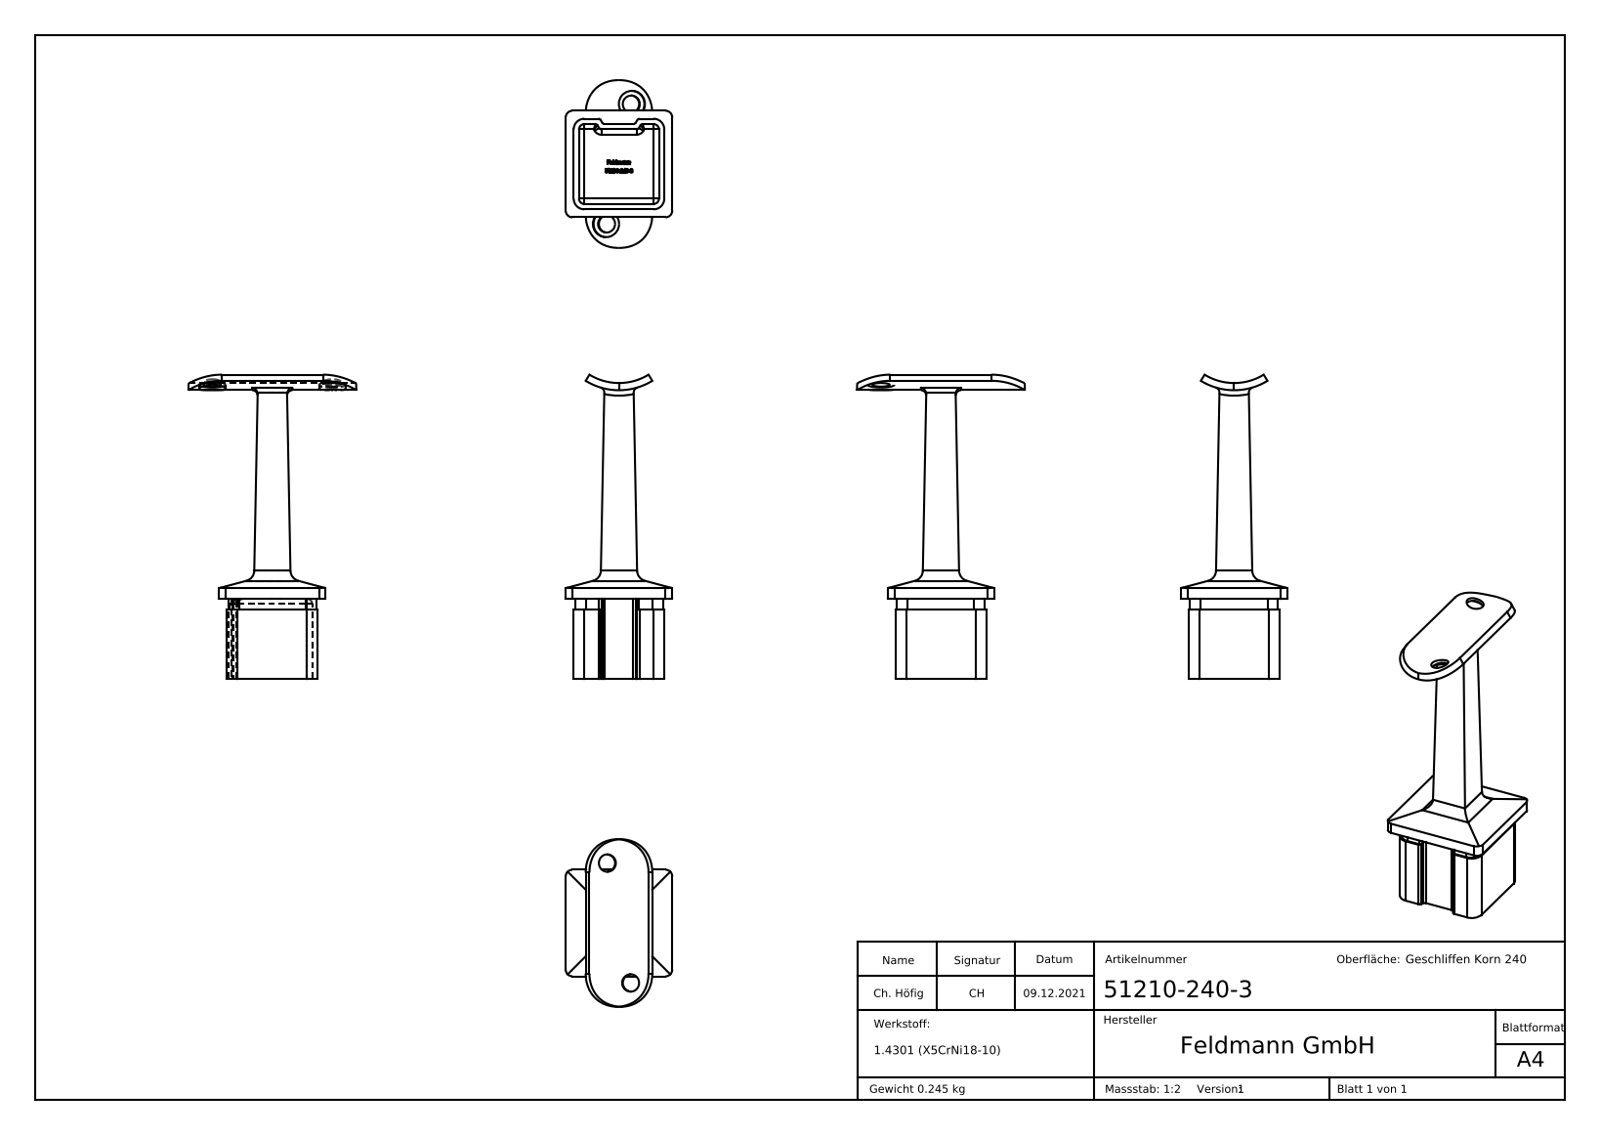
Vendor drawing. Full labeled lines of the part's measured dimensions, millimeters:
Part name (STEP PRODUCT): 51210-240-3
STEP written by: SolidWorks 2018 (CONFIG_CONTROL_DESIGN)
Units: millimetres
Bodies: 1 solid, 334 faces (174 planar, 50 cylindrical, 110 other)
Overall size (bounding box): 114.13 × 63 × 40
Volume: 31 044 mm³ · Surface area: 17 766 mm²
Round holes (diameter × count): ⌀6.5 ×2, ⌀10 ×2
Partial cylindrical surfaces — rounded edges, fillets, slot ends (radius × count): R2 ×13, R4 ×12, R1 ×10, R2.5 ×4, R12.5 ×4, R21.2 ×1, R23.9 ×1
Main face-to-face distances: 2, 32, 30, 34, 3, 5, 35, 37, 3.5, 28
